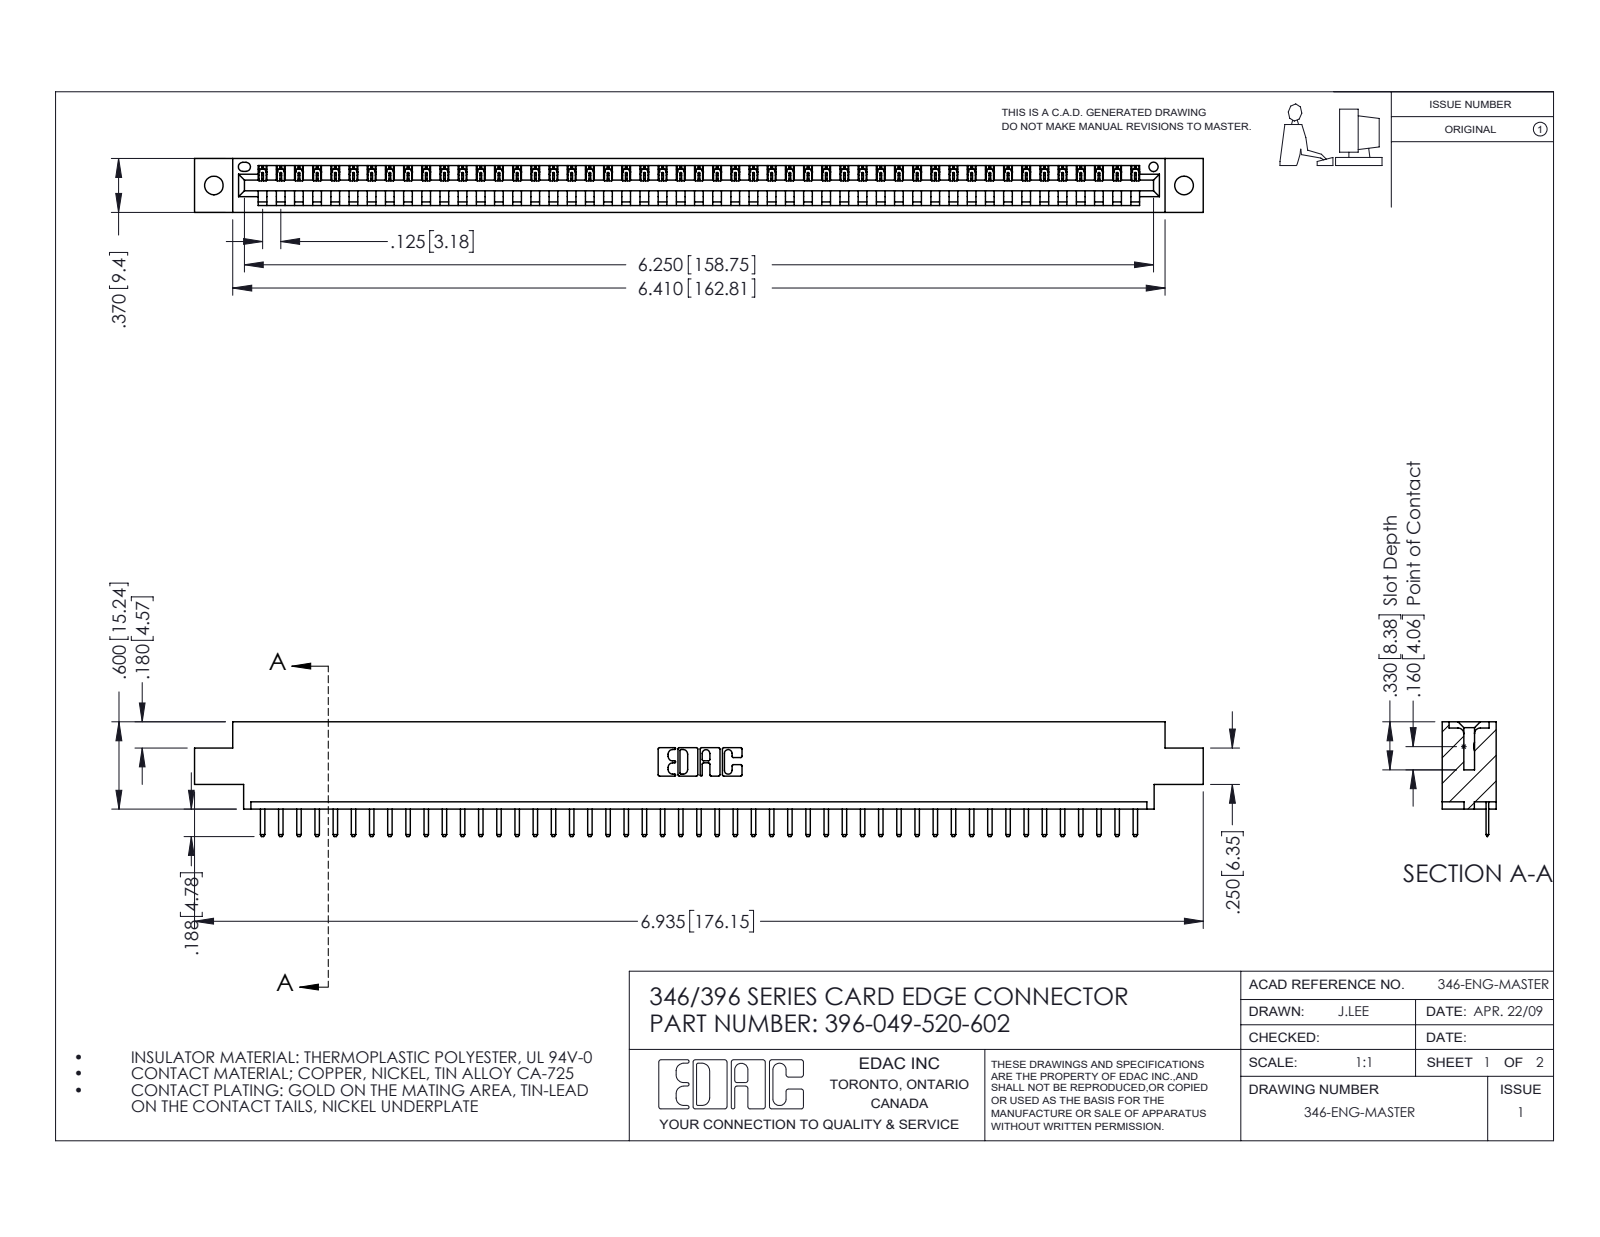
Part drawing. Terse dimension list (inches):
name: 346 Part_0.170 Offset - 0.128 Dia; 345-292-001_345-293-120; 396-049-520-602
written by: SolidWorks 2016 (CONFIG_CONTROL_DESIGN)
unit: in
bodies: 50 solids, 3164 faces (2138 planar, 1026 cylindrical, 0 other)
size: 6.935 × 0.788 × 0.37
volume: 1.012 in³; area: 31.33 in²
holes: 2× ⌀0.128, 1× ⌀0.064
rounds: 100× R0.01, 98× R0.006, 22× R0.01, 6× R0.007, 6× R0.031, 3× R0.026, 2× R0.031, 2× R0.04
face distances: 0.048, 0.322, 0.37, 0.25, 0.148, 0.222, 0.1, 0.174, 0.072, 0.298
hole spacings: 0.246, 6.461, 6.67
